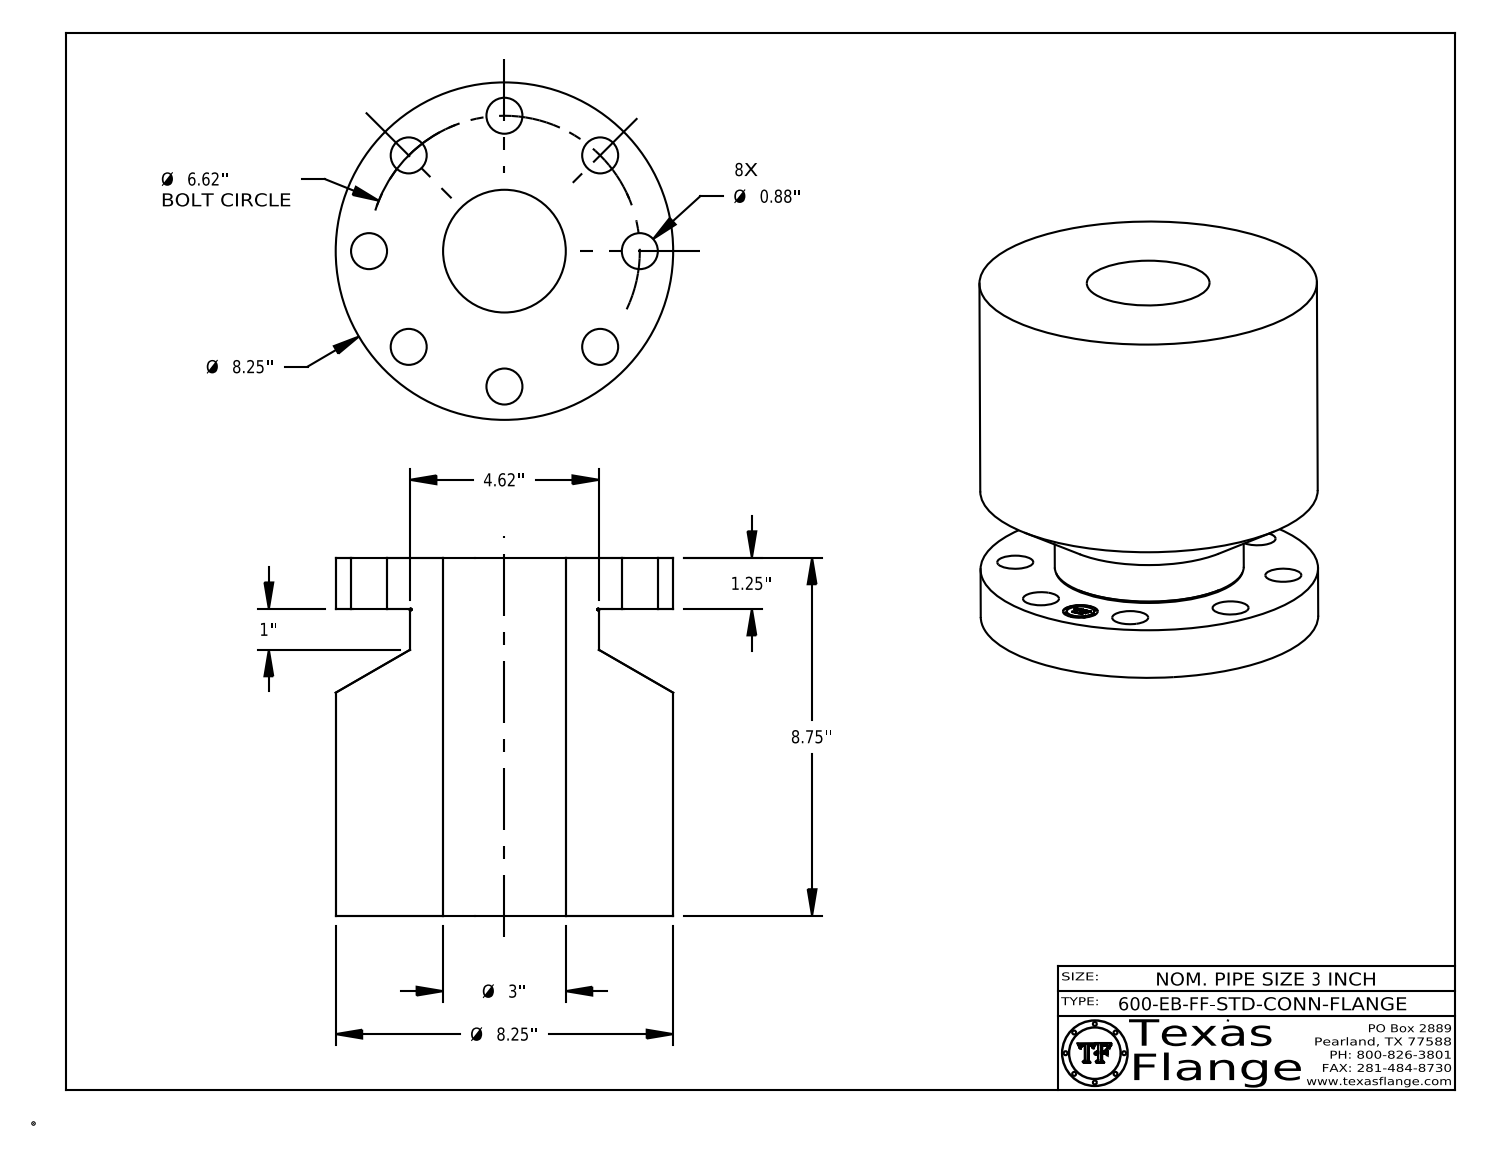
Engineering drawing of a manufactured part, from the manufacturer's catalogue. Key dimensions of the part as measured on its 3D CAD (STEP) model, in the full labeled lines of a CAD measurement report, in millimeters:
Part name (STEP PRODUCT): 3-600-EB-FF-STD-CONN-FLANGE
STEP written by: CATIA V5 STEP AP214 (AUTOMOTIVE_DESIGN)
Units: millimetres
Bodies: 1 solid, 418 faces (368 planar, 44 cylindrical, 6 other)
Overall size (bounding box): 222.3 × 209.6 × 209.6
Volume: 5 606 000 mm³ · Surface area: 297 500 mm²
Round holes (diameter × count): ⌀22.4 ×8, ⌀21.6 ×1, ⌀76.2 ×1
Round bosses / shafts (diameter × count): ⌀1.3 ×8, ⌀209.6 ×1, ⌀117.3 ×1, ⌀17 ×1
Main face-to-face distances: 222.3, 31.8, 190.5, 31.6, 190.6, 0.4, 6.5, 6.3, 1.2, 4.2
Hole centre spacings: 84.1, 64.3, 155.3, 118.9, 118.9, 32.8, 93.4, 164.9
